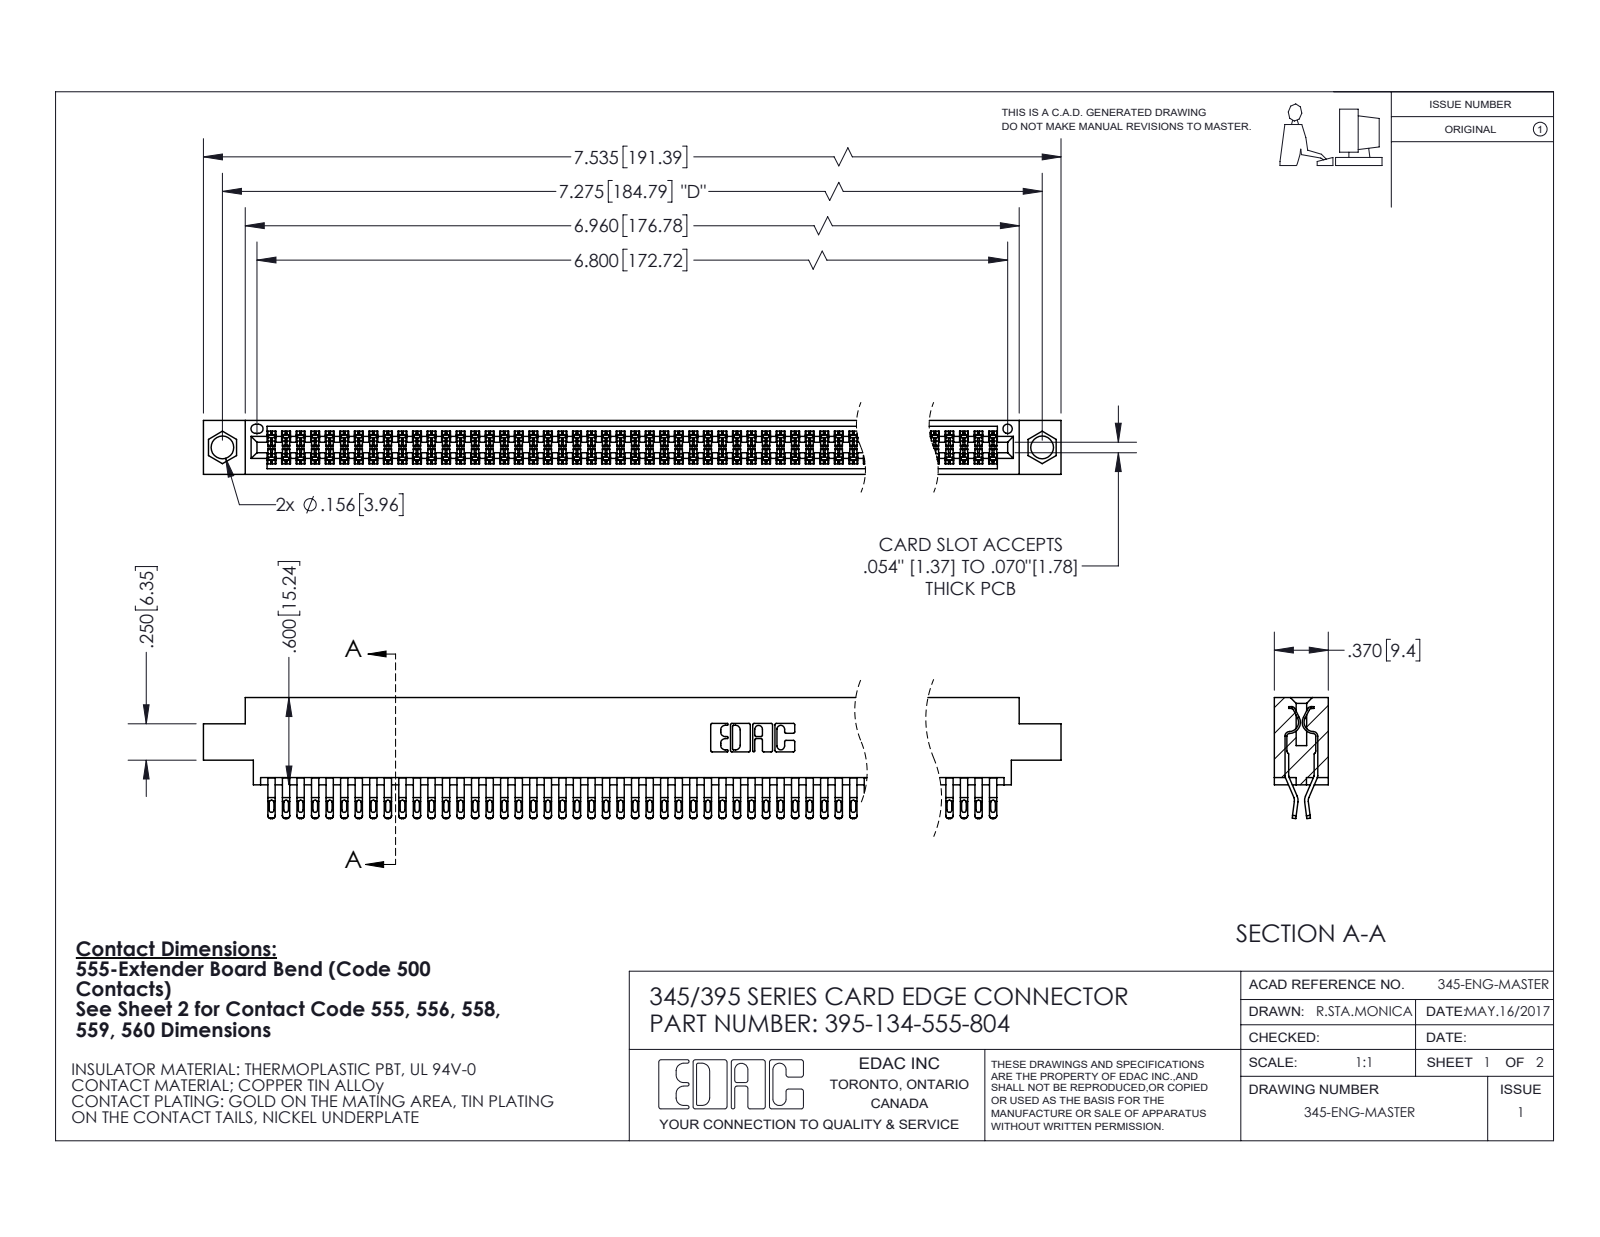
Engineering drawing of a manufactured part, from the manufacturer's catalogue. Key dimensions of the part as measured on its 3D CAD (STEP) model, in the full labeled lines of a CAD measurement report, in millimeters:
Part name (STEP PRODUCT): 395-134-555-804; 345-292-001_555 Tail; 345 Part_0.170 Offset - 0.156 Dia-TI
STEP written by: SolidWorks 2020 (CONFIG_CONTROL_DESIGN)
Units: millimetres
Bodies: 135 solids, 7648 faces (4252 planar, 3396 cylindrical, 0 other)
Overall size (bounding box): 191.4 × 21.1 × 9.4
Volume: 18 990 mm³ · Surface area: 29 900 mm²
Round holes (diameter × count): ⌀4 ×2, ⌀1.6 ×1
Partial cylindrical surfaces — rounded edges, fillets, slot ends (radius × count): R0.4 ×335, R0.2 ×268, R0.5 ×268, R0.3 ×22, R0.2 ×6, R0.8 ×6, R0.7 ×3, R0.3 ×2
Main face-to-face distances: 1.8, 7.6, 0.6, 9.4, 5.1, 2.5, 6.9, 5.7, 4.4, 3.8
Hole centre spacings: 6.9, 178.8, 184.8
